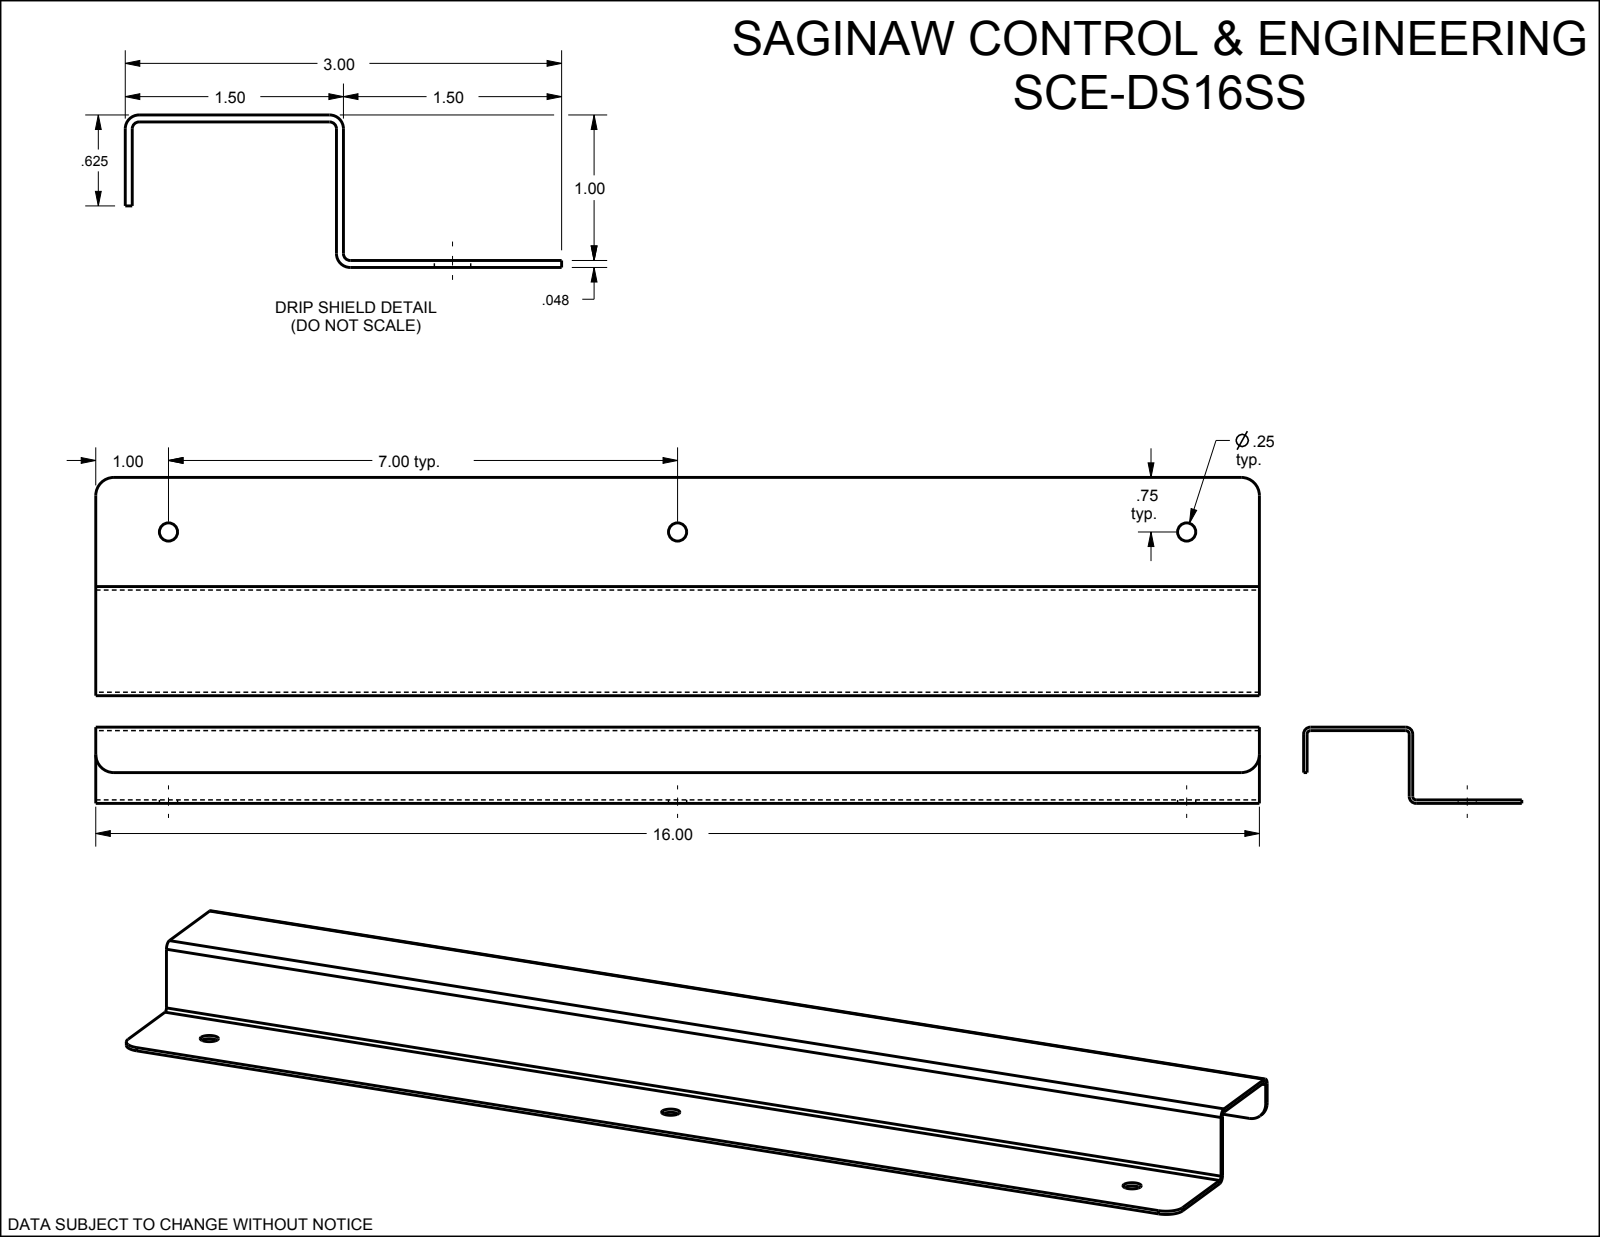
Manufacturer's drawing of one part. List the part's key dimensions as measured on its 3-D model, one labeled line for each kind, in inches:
Part name (STEP PRODUCT): SCE-DS16SS6
STEP written by: SolidWorks 2019 (CONFIG_CONTROL_DESIGN)
Units: inches
Bodies: 1 solid, 25 faces (12 planar, 13 cylindrical, 0 other)
Overall size (bounding box): 16 × 3 × 1.048
Volume: 3.435 in³ · Surface area: 145.2 in²
Round holes (diameter × count): ⌀0.25 ×3
Partial cylindrical surfaces — rounded edges, fillets, slot ends (radius × count): R0.25 ×4, R0.047 ×3, R0.095 ×3
Main face-to-face distances: 0.048, 1, 0.952, 1.048, 1.452, 1.5, 1.404, 0.423, 0.375, 0.577
Hole centre spacings: 7, 14
